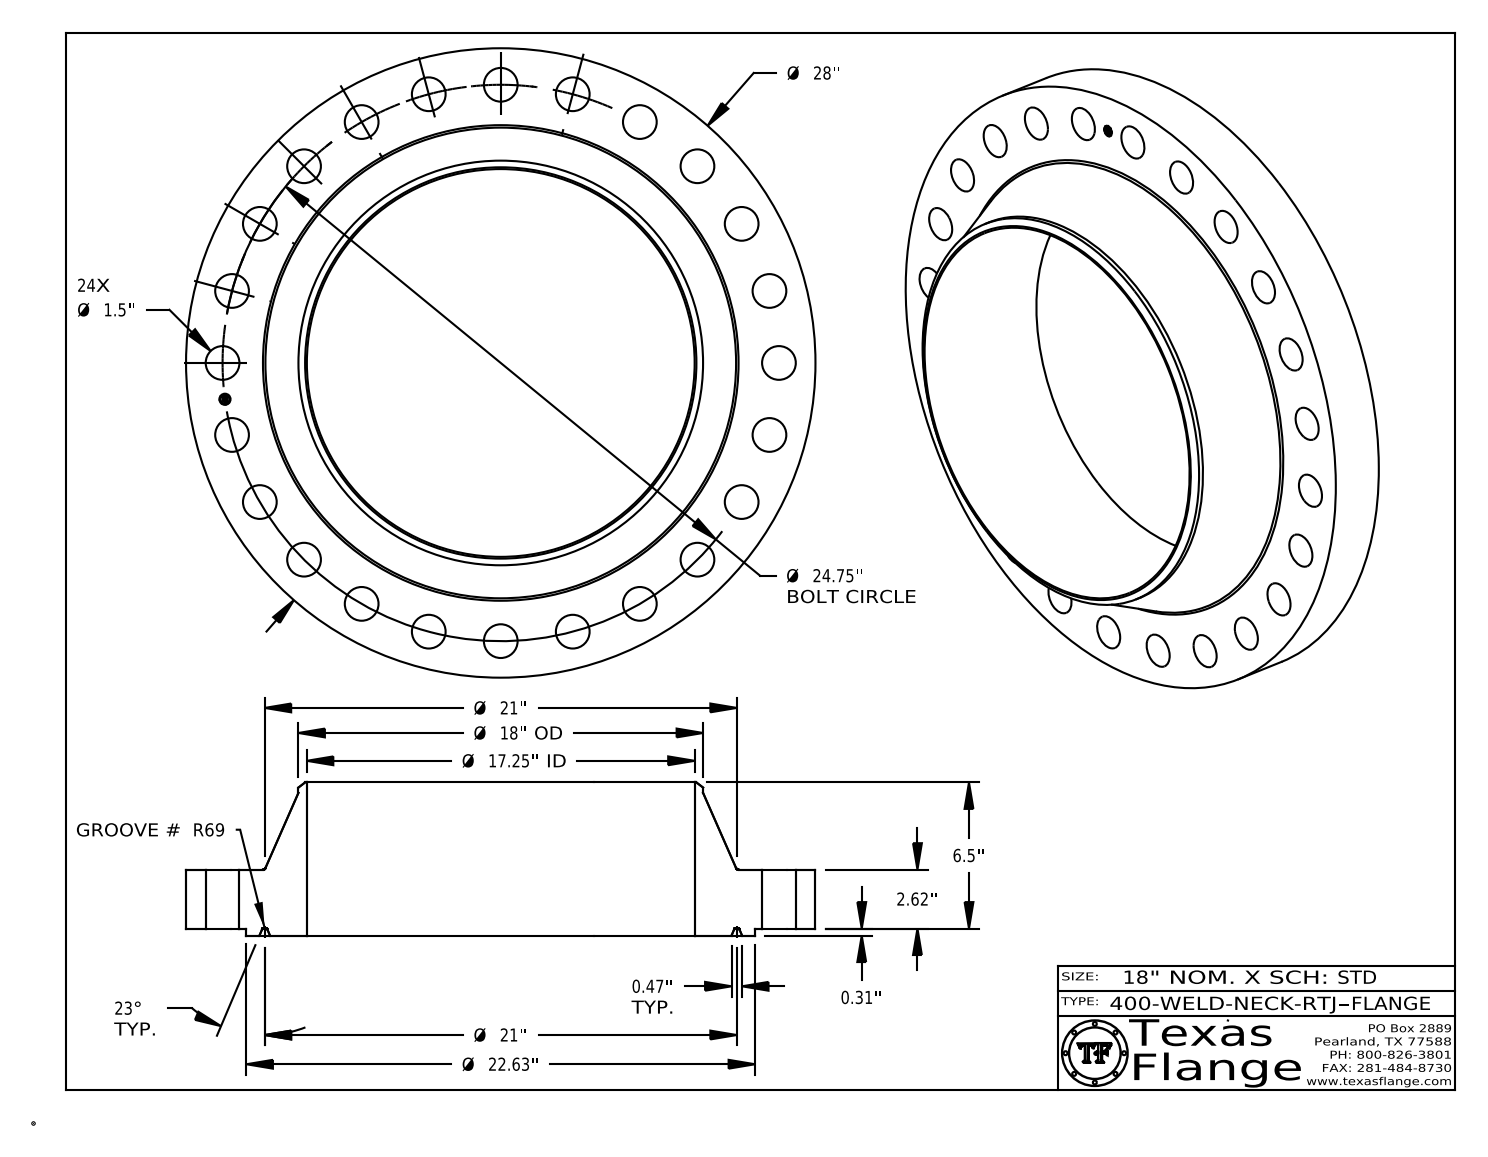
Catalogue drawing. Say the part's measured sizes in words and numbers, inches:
The part is named "400-WELD-NECK-RTJ". Its 3-D file was written by "CATIA V5 STEP AP214 (AUTOMOTIVE_DESIGN)". It is 1 solid with 461 faces: 371 planar, 76 cylindrical and 14 other. Overall it measures 28 by 28 by 6.813 inches. Its volume is 1 167 cubic inches and its surface area 1 777 square inches. Round holes: 24 of diameter 1.5, 1 of diameter 0.495, 1 of diameter 17.25. Round bosses or shafts: 8 of diameter 0.03, 1 of diameter 28, 1 of diameter 22.625, 1 of diameter 18, 1 of diameter 0.39. The main face-to-face distances are 2.62, 0.313, 2.933, 6.813, 6.5, 3.88, 2.918, 2.605, 0.015, 3.895. The hole center spacings are 12.375, 9.471, 15.067, 17.501, 21.434, 22.866, 23.906, 3.23.
